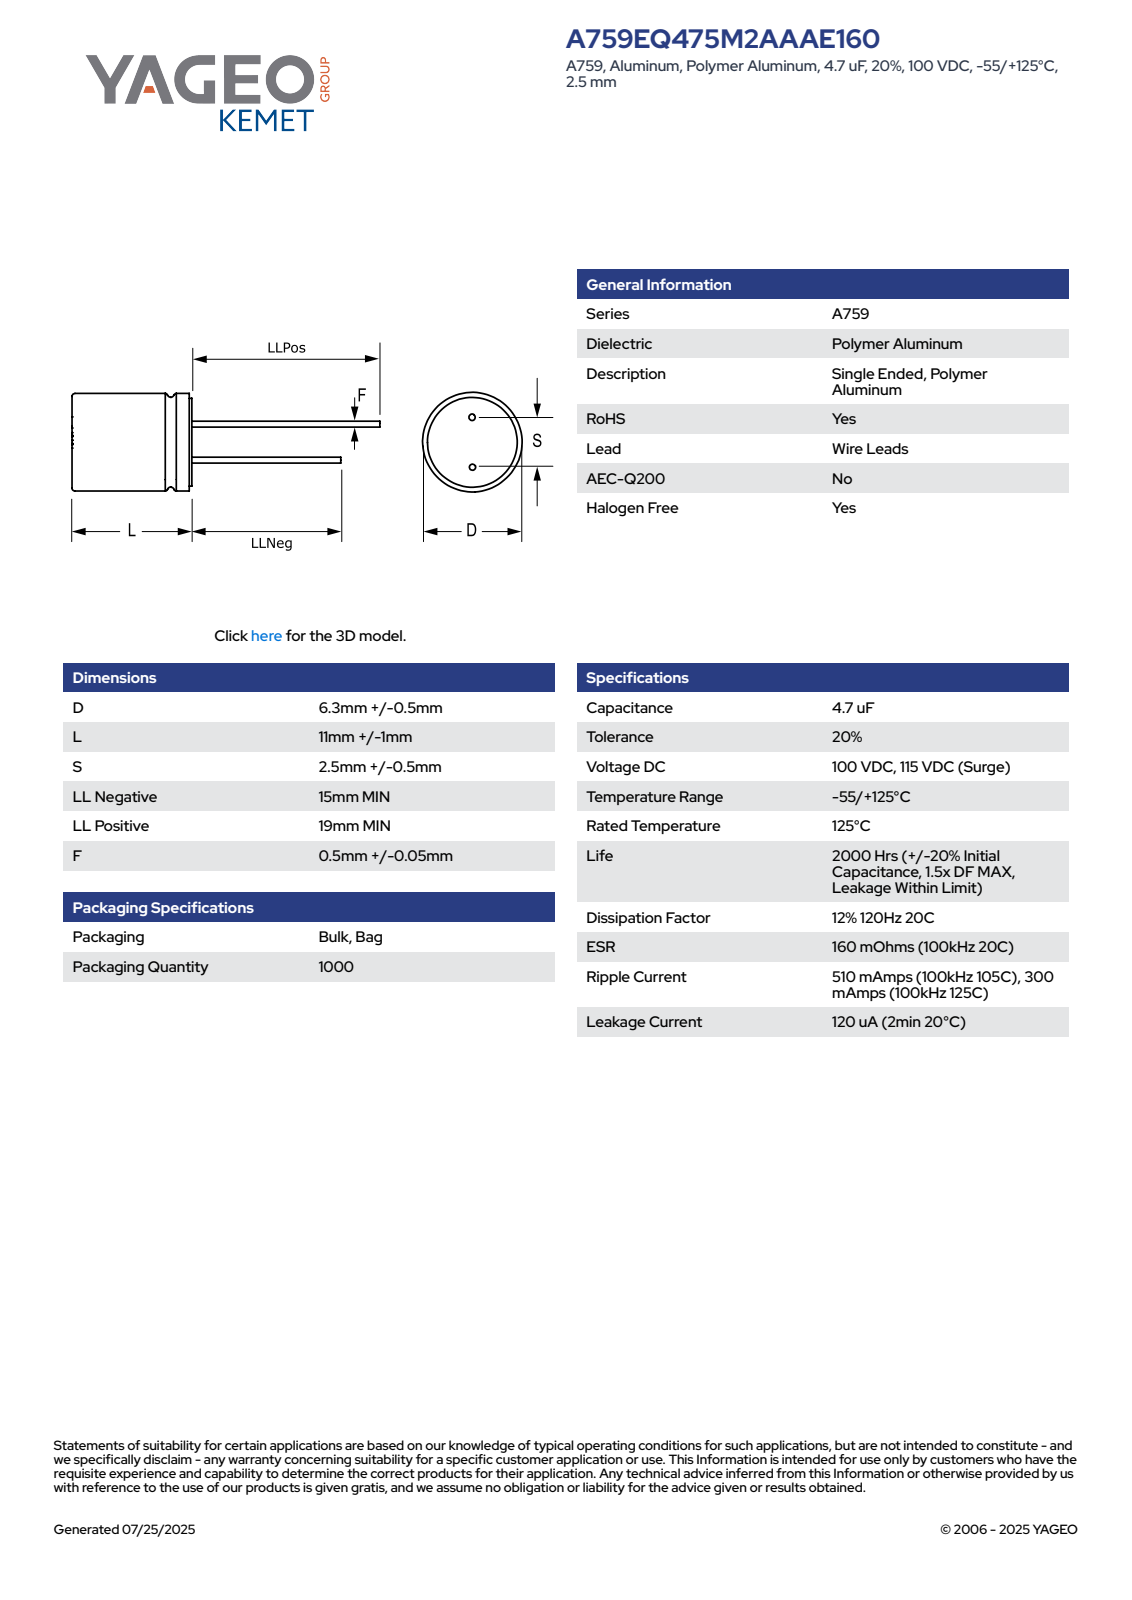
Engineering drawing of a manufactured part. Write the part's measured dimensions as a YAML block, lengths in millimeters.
part_name: "CAR_KP_6.3X11_D6.8L12S2.5F0.55"
step_written_by: "SolidWorks 2014 (AUTOMOTIVE_DESIGN)"
units: millimeters
bodies: {solids: 4, faces: 75, planar: 61, cylindrical: 8, other: 6}
overall_size: [31, 6.8, 6.8]
volume: 439
surface_area: 397
round_bosses_or_shafts:
  - {diameter: 0.55, count: 2}
  - {diameter: 6.8, count: 1}
face_to_face_distances: [12, 12.01, 27.01, 31.01, 27, 31, 15, 19, 4, 0.75]
